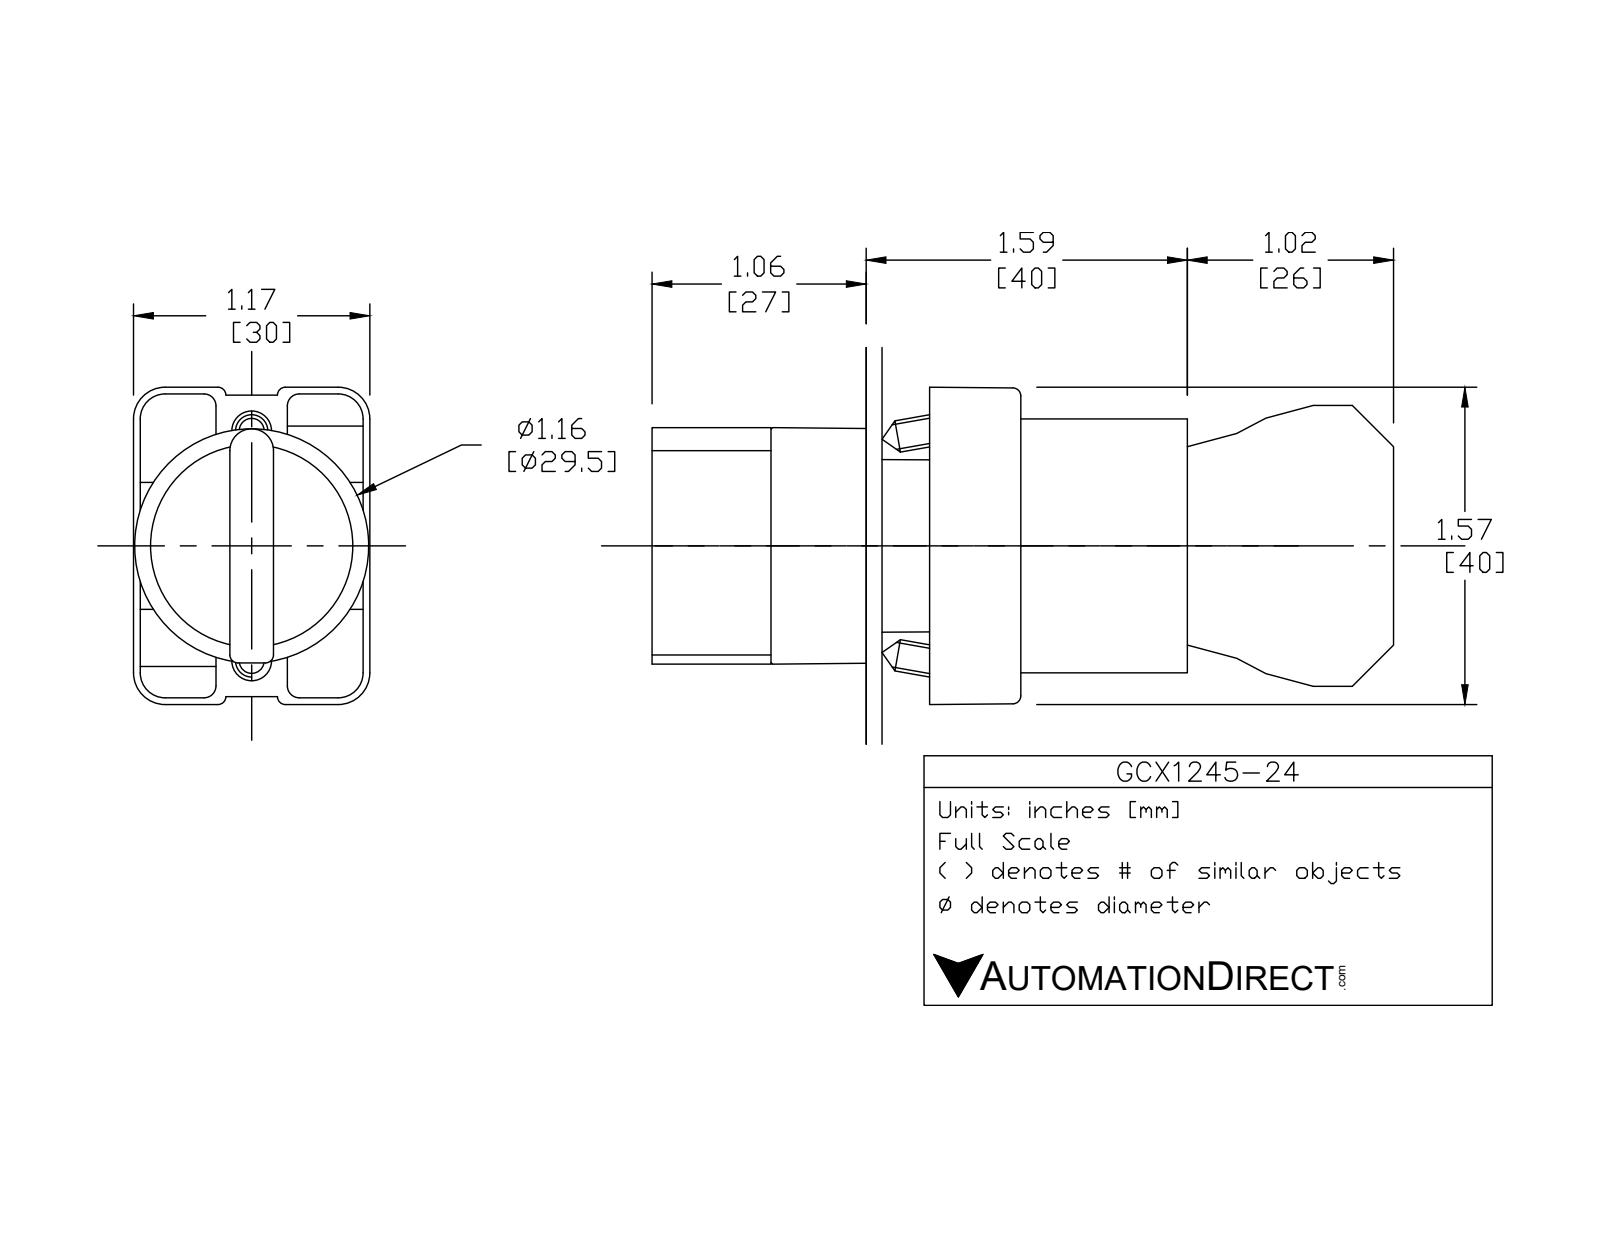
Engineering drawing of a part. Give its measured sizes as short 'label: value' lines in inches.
name: ecx1029; GCX1245-24; ecx1040; ECX1050 (+1 more)
written by: SolidWorks 2016 (AUTOMOTIVE_DESIGN)
unit: in
bodies: 8 solids, 445 faces (263 planar, 151 cylindrical, 31 other)
size: 3.653 × 1.581 × 1.177
volume: 2.799 in³; area: 39 in²
holes: 2× ⌀0.079, 2× ⌀0.124, 2× ⌀0.13, 1× ⌀0.087, 1× ⌀0.197, 1× ⌀0.469, 1× ⌀0.878, 1× ⌀0.888, 1× ⌀1.024
bosses: 4× ⌀0.157, 1× ⌀1.175, 1× ⌀1.004, 1× ⌀0.945, 1× ⌀0.856, 1× ⌀0.78, 1× ⌀0.504
rounds: 24× R0.059, 12× R0.041, 12× R0.124, 12× R0.157, 9× R0.039, 2× R0.128, 1× R0.02, 1× R0.063
face distances: 0.827, 2.02, 1.193, 0.579, 1.244, 1.171, 0.472, 0.469, 0.031, 0.033
hole spacings: 0.236, 0.544, 0.472, 0.49
